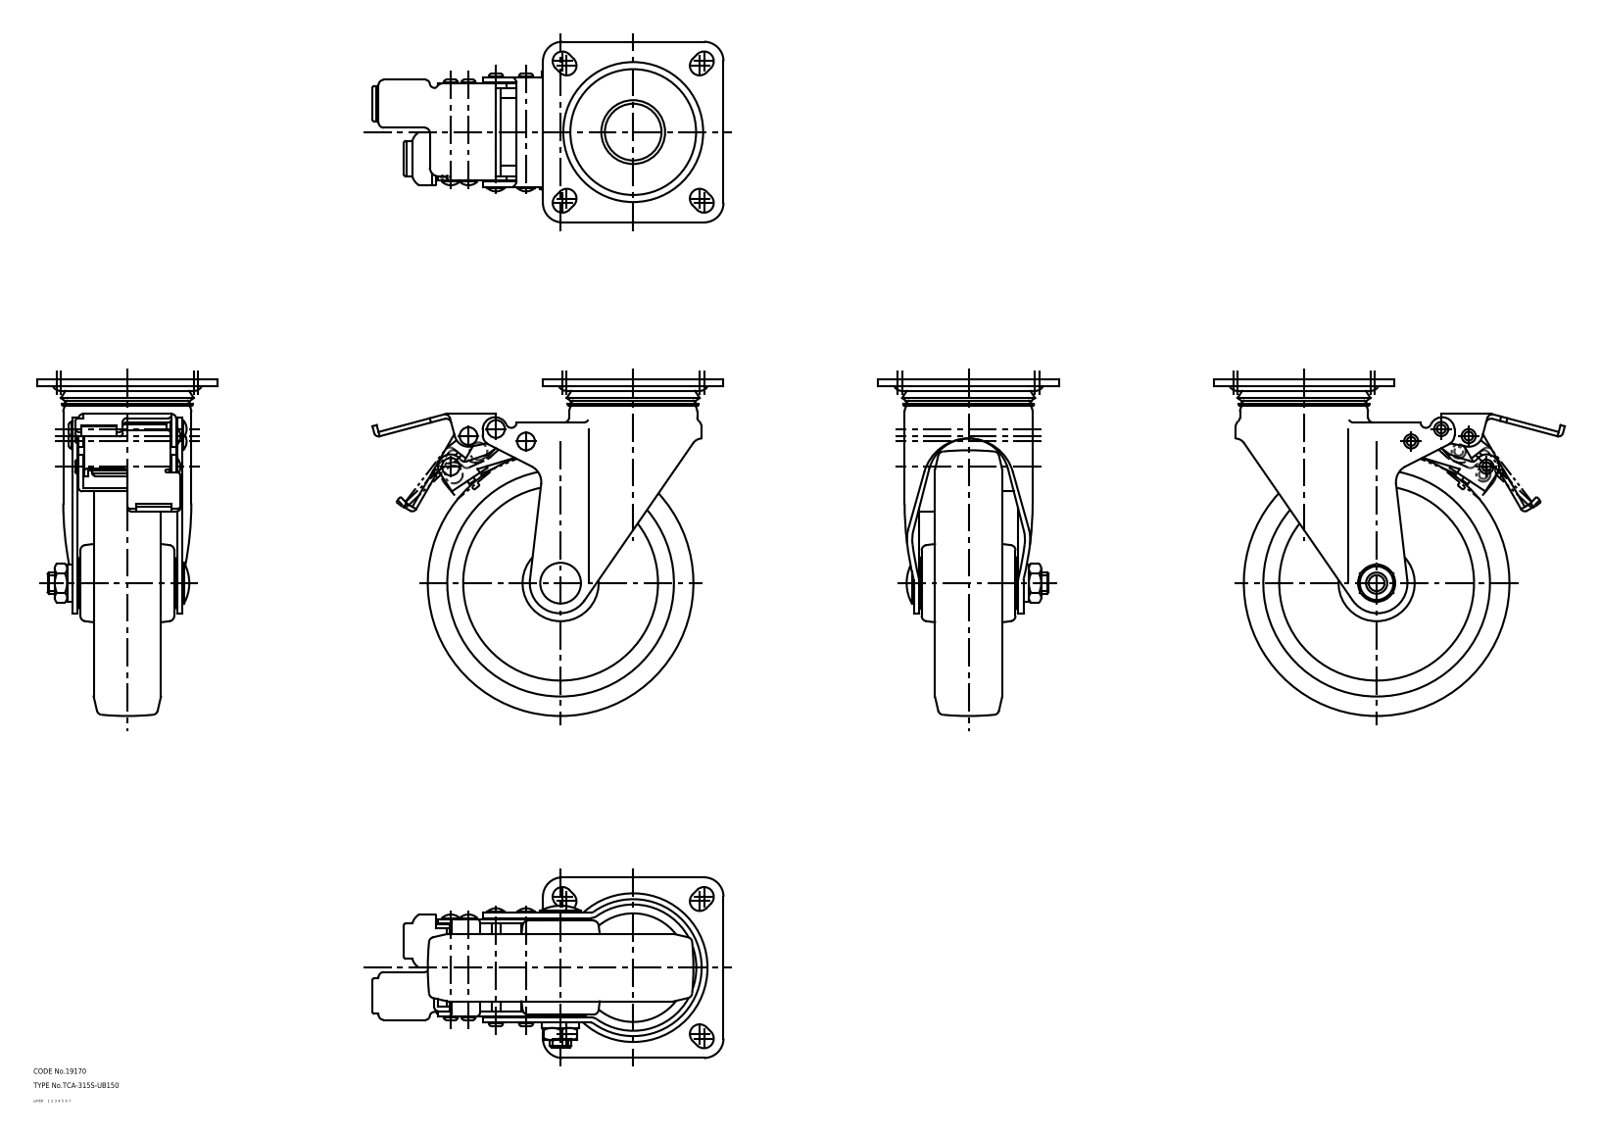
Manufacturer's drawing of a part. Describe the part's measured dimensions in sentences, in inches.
The part is named "lever; wheel; mounting plate; main shaft (+2 more)". Its 3-D file was written by "CADfix (AUTOMOTIVE_DESIGN)". It is 6 solids with 439 faces: 0 planar, 0 cylindrical and 439 other. Overall it measures 7.806 by 7.48 by 4.016 inches. Its volume is 43.9 cubic inches and its surface area 255.7 square inches.
